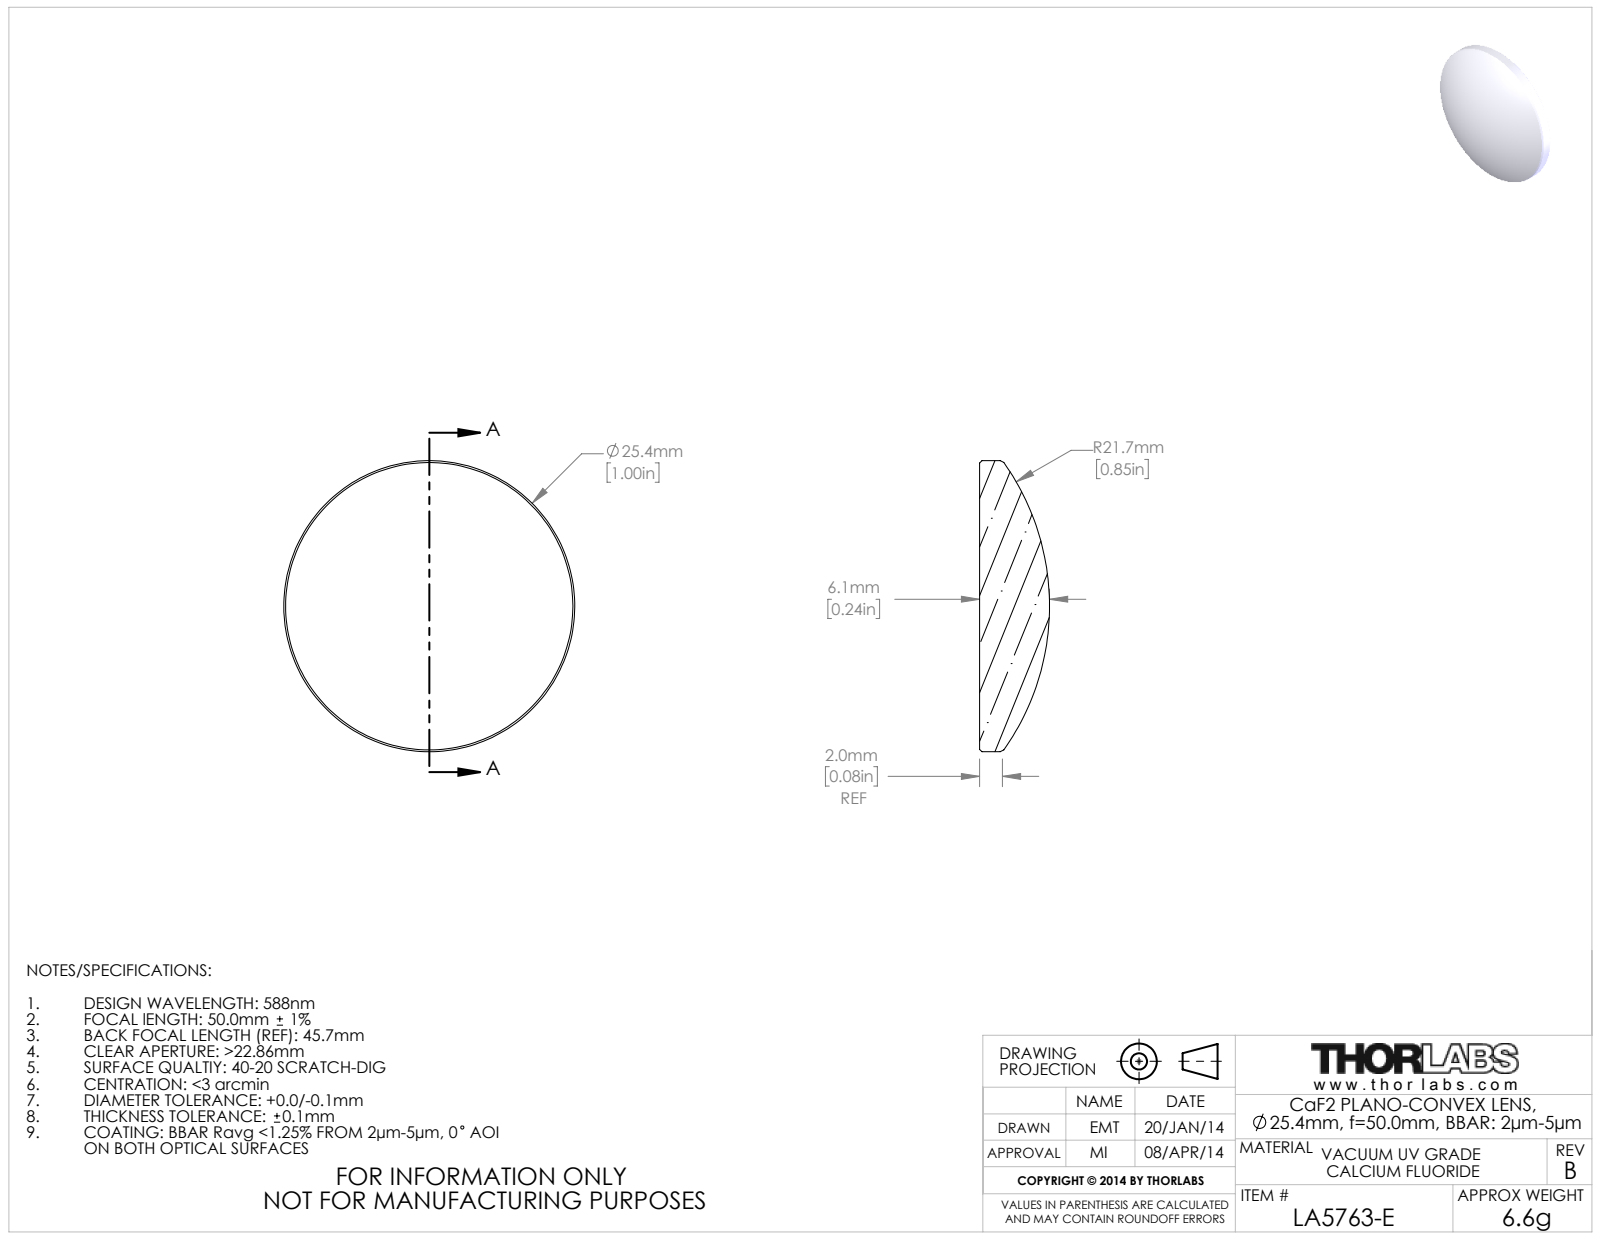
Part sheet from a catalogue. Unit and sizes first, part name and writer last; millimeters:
Units: millimetres
Overall size (bounding box): 25.4 × 25.4 × 6.1
Round bosses / shafts (diameter × count): ⌀25.4 ×1
Volume: 2 084 mm³ · Surface area: 1 212 mm²
Bodies: 1 solid, 9 faces (1 planar, 2 cylindrical, 6 other)
Part name (STEP PRODUCT): 20132-E0W
STEP written by: SolidWorks 2018 (CONFIG_CONTROL_DESIGN)
